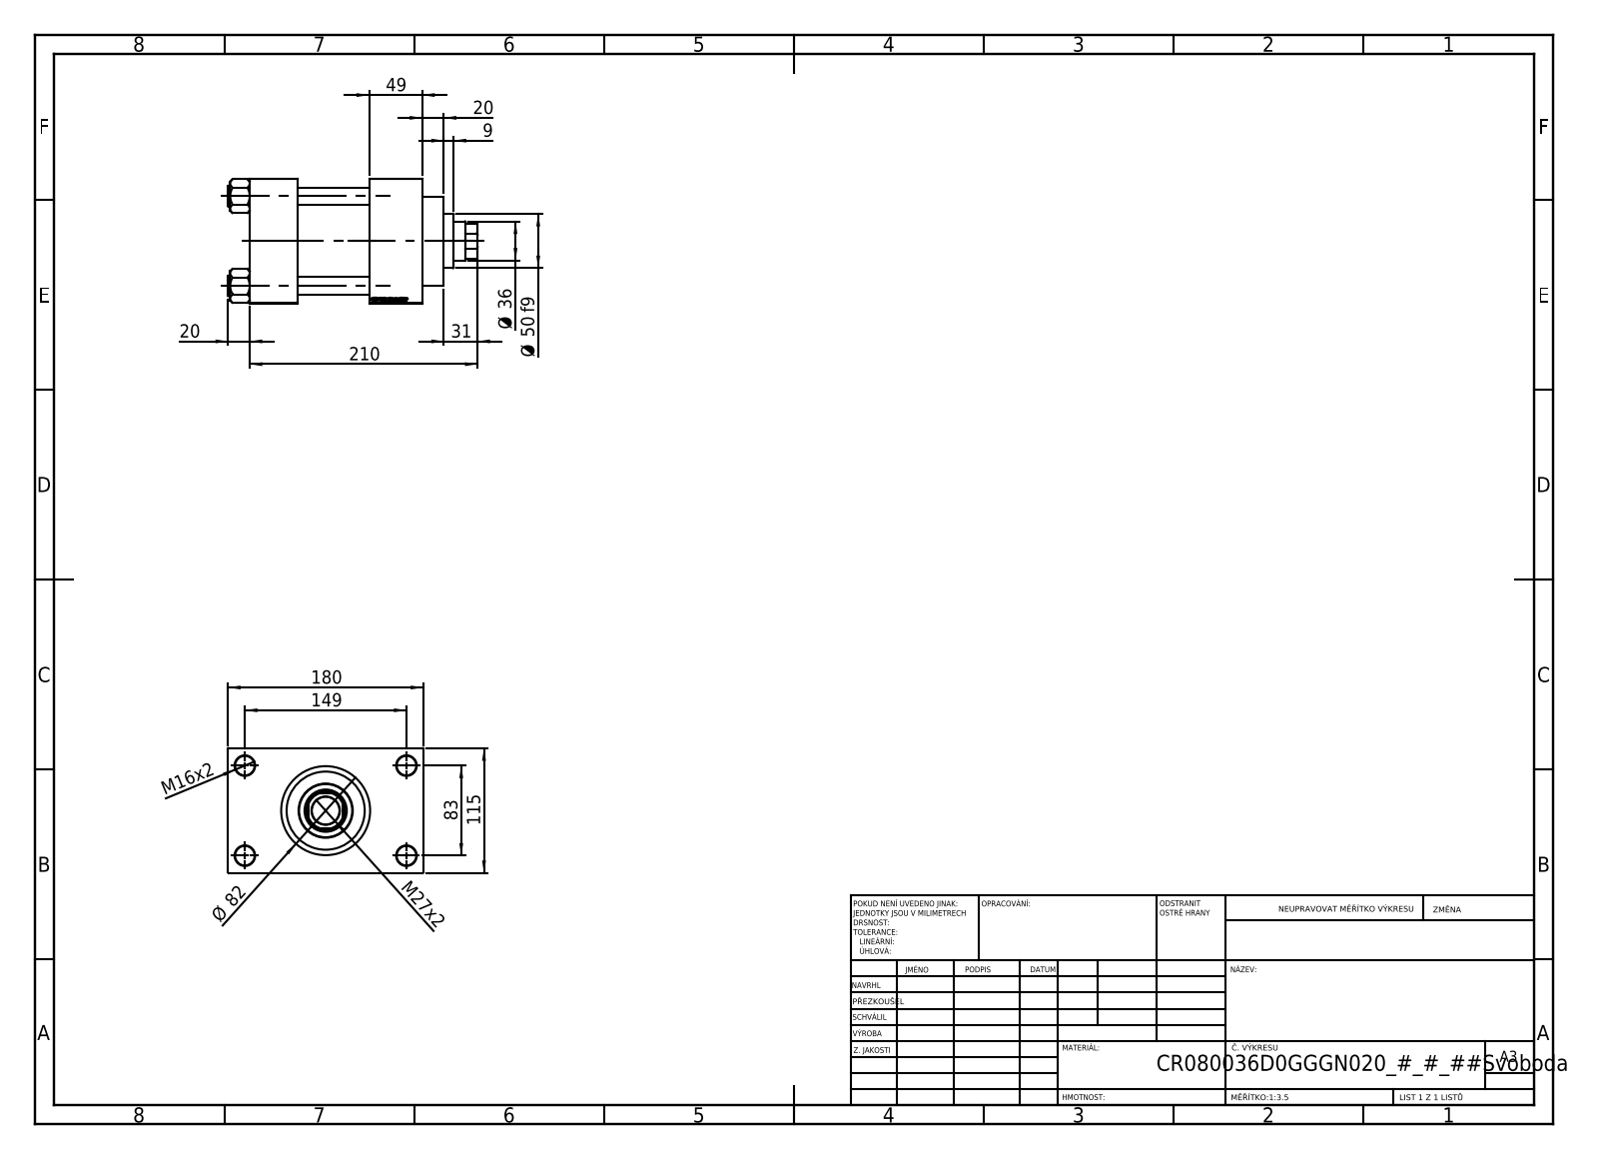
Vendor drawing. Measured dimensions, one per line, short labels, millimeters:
name: V215CR_D_TYCINKA; V215CR_VCP_D; V215_VC_A; V215CR_D_Body (+1 more)
written by: SolidWorks 2019 (CONFIG_CONTROL_DESIGN)
unit: mm
bodies: 11 solids, 1152 faces (545 planar, 89 cylindrical, 518 other)
size: 230 × 180 × 115
volume: 1 997 000 mm³; area: 293 903 mm²
holes: 4× ⌀16, 4× ⌀18, 2× ⌀7, 2× ⌀26.44, 2× ⌀35, 1× ⌀25.5, 1× ⌀36, 1× ⌀39, 1× ⌀61, 1× ⌀72, 1× ⌀80
bosses: 4× ⌀19, 1× ⌀86, 1× ⌀82, 1× ⌀50
rounds: 1× R17.5
face distances: 115, 66, 110, 49, 44, 159, 32.5, 147.5, 20, 69
hole spacings: 33.15, 58.48, 82.7, 85.28, 89.24, 115.85, 142.43, 83
